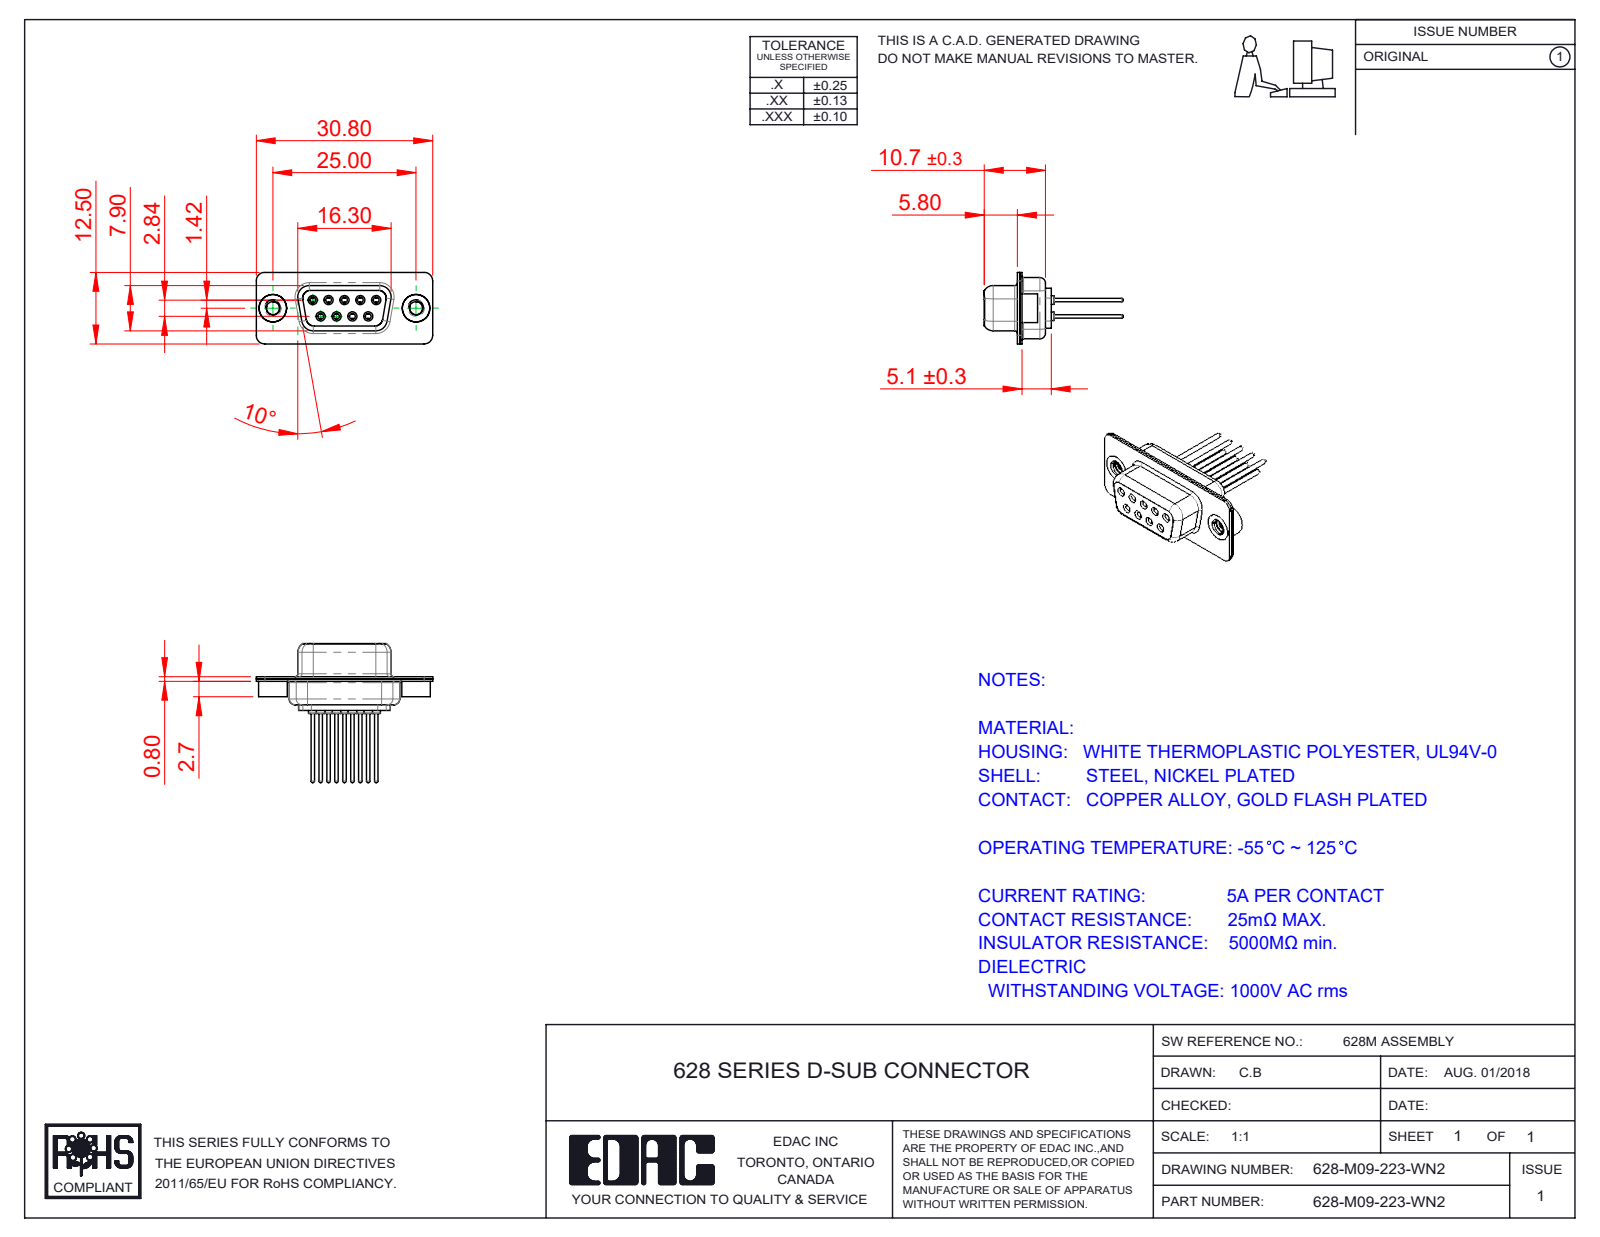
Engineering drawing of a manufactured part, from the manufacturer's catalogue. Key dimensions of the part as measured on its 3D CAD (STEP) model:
Part name (STEP PRODUCT): 628M Contact Row 1_23; 628M 4-40 Threaded Rivet; 628-M09-223-WN2; 628M Shell Front_09 Contacts (+3 more)
STEP written by: SolidWorks 2020 (CONFIG_CONTROL_DESIGN)
Units: millimetres
Bodies: 14 solids, 774 faces (202 planar, 308 cylindrical, 264 other)
Overall size (bounding box): 30.8 × 24.27 × 12.5
Volume: 1 721 mm³ · Surface area: 4 540 mm²
Round holes (diameter × count): ⌀1 ×9, ⌀1.1 ×9, ⌀1.7 ×9, ⌀1.8 ×9, ⌀2 ×9, ⌀2.26 ×2, ⌀4 ×2, ⌀4.8 ×2
Round bosses / shafts (diameter × count): ⌀2.2 ×9, ⌀1.6 ×9, ⌀1.5 ×9, ⌀0.6 ×9, ⌀5 ×2, ⌀4.9 ×2
Partial cylindrical surfaces — rounded edges, fillets, slot ends (radius × count): R1.5 ×16, R2 ×12, R1.35 ×8, R1.6 ×8, R0.25 ×4, R0.5 ×4, R0.6 ×4, R0.65 ×4
Main face-to-face distances: 0.4, 1.4, 0.45, 8.45, 0.8, 1, 8.9, 1.8, 6.2, 7.05
Hole centre spacings: 3.16, 2.77, 5.54, 5.03, 5.04, 8.31, 7.1, 7.48
